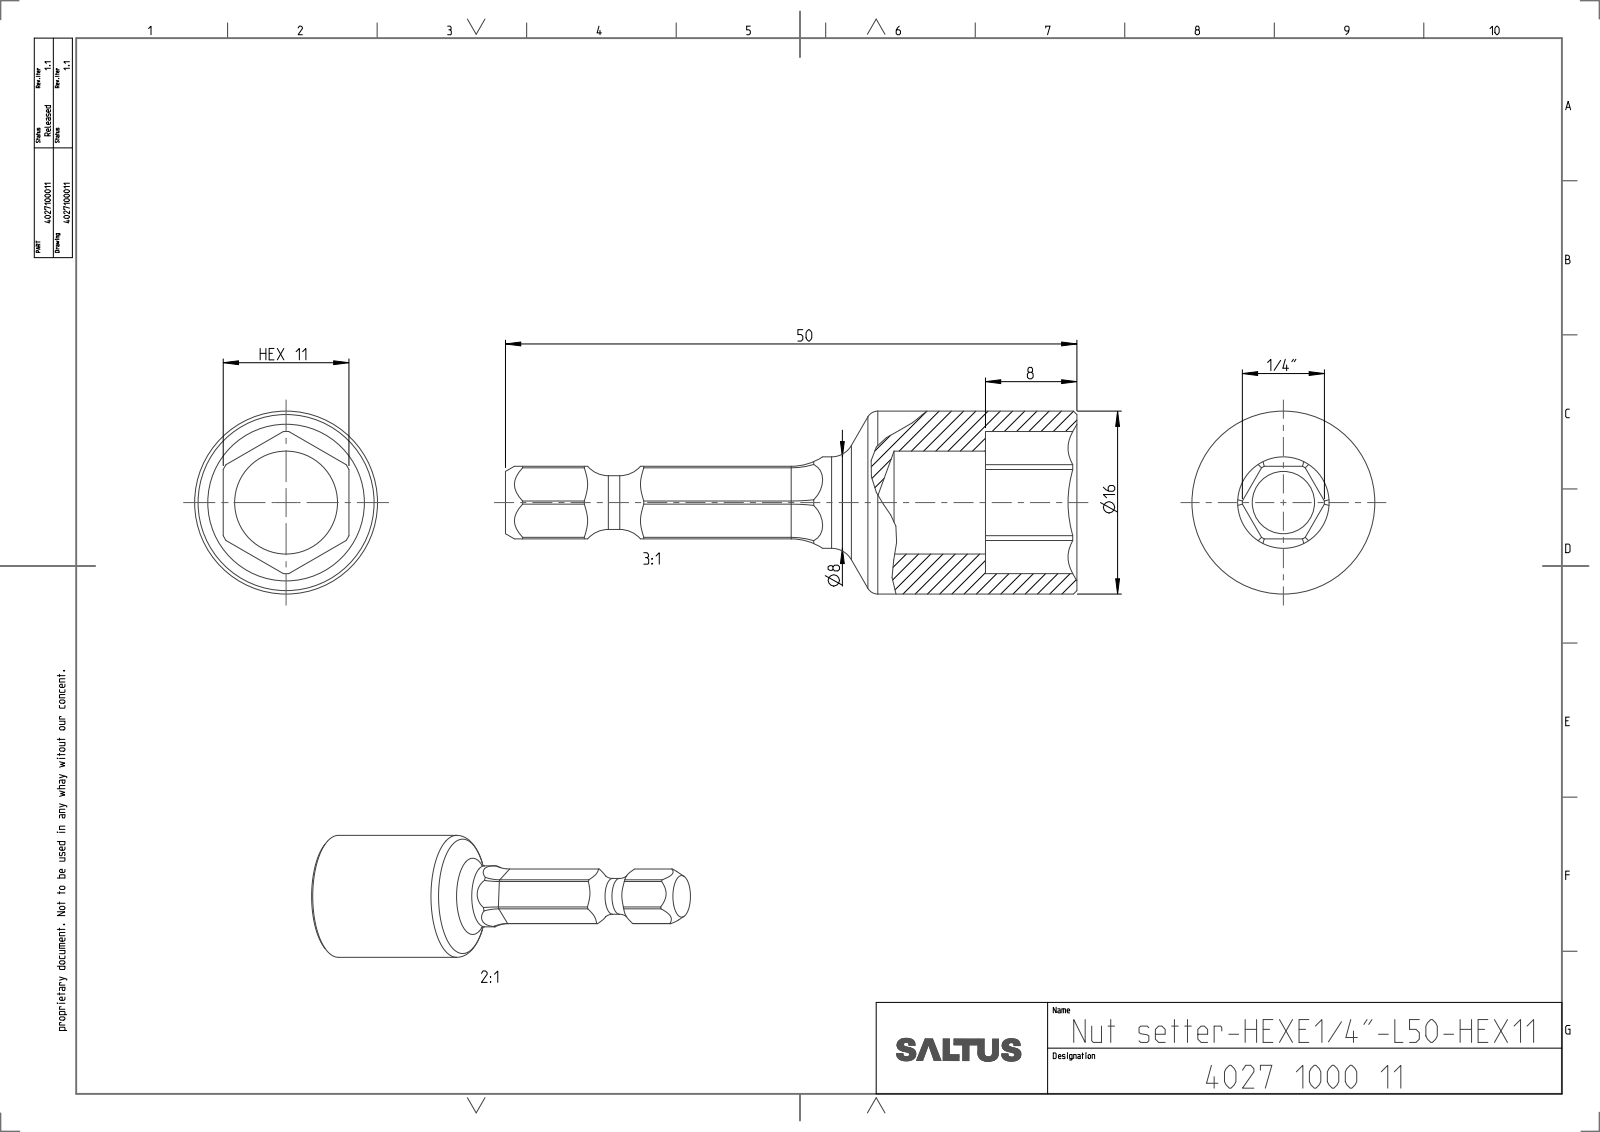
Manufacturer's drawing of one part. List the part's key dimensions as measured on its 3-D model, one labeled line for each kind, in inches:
Part name (STEP PRODUCT): 4027100011
STEP written by: CREO PARAMETRIC BY PTC INC, 2022414 (CONFIG_CONTROL_DESIGN)
Units: inches
Bodies: 1 solid, 77 faces (21 planar, 32 cylindrical, 24 other)
Overall size (bounding box): 1.969 × 0.63 × 0.63
Volume: 0.214 in³ · Surface area: 3.787 in²
Round holes (diameter × count): ⌀0.354 ×1
Round bosses / shafts (diameter × count): ⌀0.63 ×1, ⌀0.315 ×1, ⌀0.185 ×1
Partial cylindrical surfaces — rounded edges, fillets, slot ends (radius × count): R0.197 ×6, R0.141 ×1, R0.244 ×1
Main face-to-face distances: 0.25, 0.433, 0.25, 0.315, 1.654, 1.969
